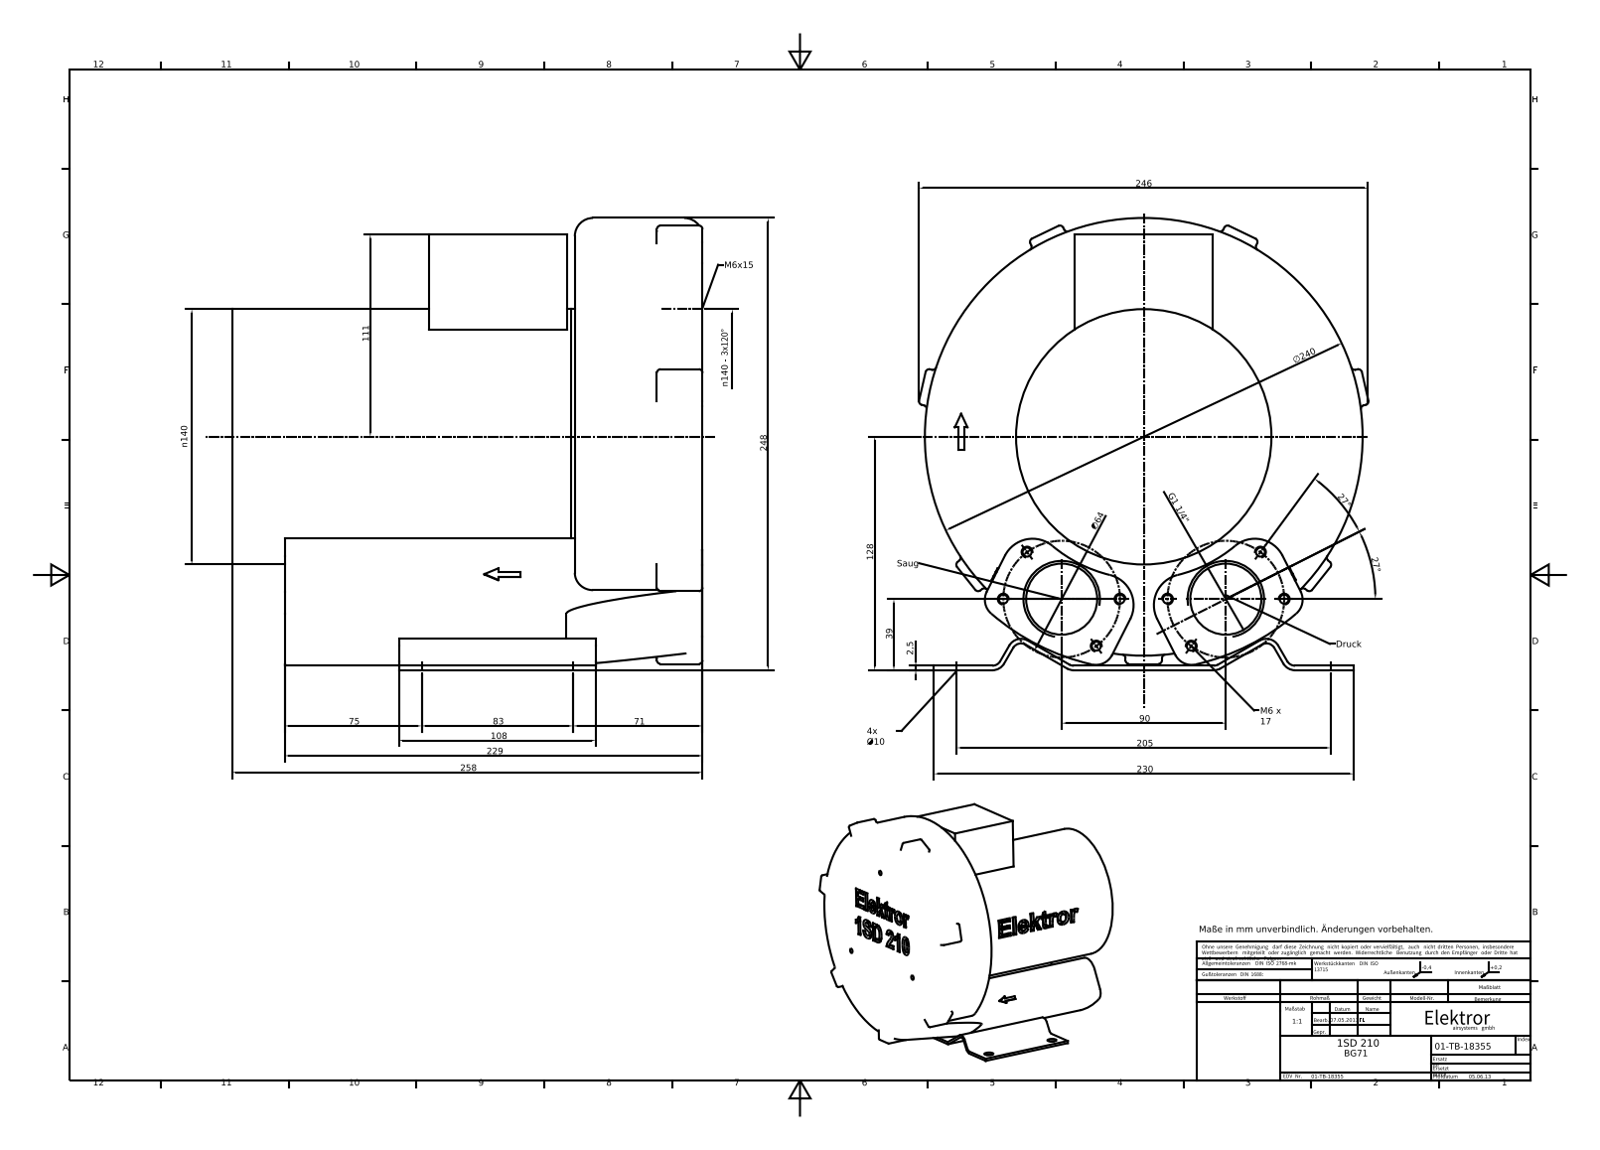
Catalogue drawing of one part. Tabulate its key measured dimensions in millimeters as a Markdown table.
| quantity | value |
| --- | --- |
| part name | 01-TB-18870 |
| STEP written by | Autodesk Inventor 2012 (CONFIG_CONTROL_DESIGN) |
| units | millimeters |
| bodies | 2 solids, 572 faces (244 planar, 116 cylindrical, 212 other) |
| overall size | 258 × 248 × 246.42 |
| volume | 7 503 000 mm³ |
| surface area | 386 618 mm² |
| round holes (diameter × count) | 4.92 × 10, 10 × 4, 38.95 × 2, 4.92 × 1 |
| round bosses / shafts (diameter × count) | 140 × 1 |
| partial cylindrical surfaces (radius × count) | 2 × 70, 5 × 6, 7.5 × 6, 10 × 4, 17 × 4, 78 × 1, 120 × 1, 128 × 1 |
| main face-to-face distances | 2.5, 70, 258, 188, 76, 76.96, 239, 236.5, 229, 159 |
| hole center spacings | 32, 28.88, 57.11, 64, 90, 121.24, 28.43, 46.77 |
